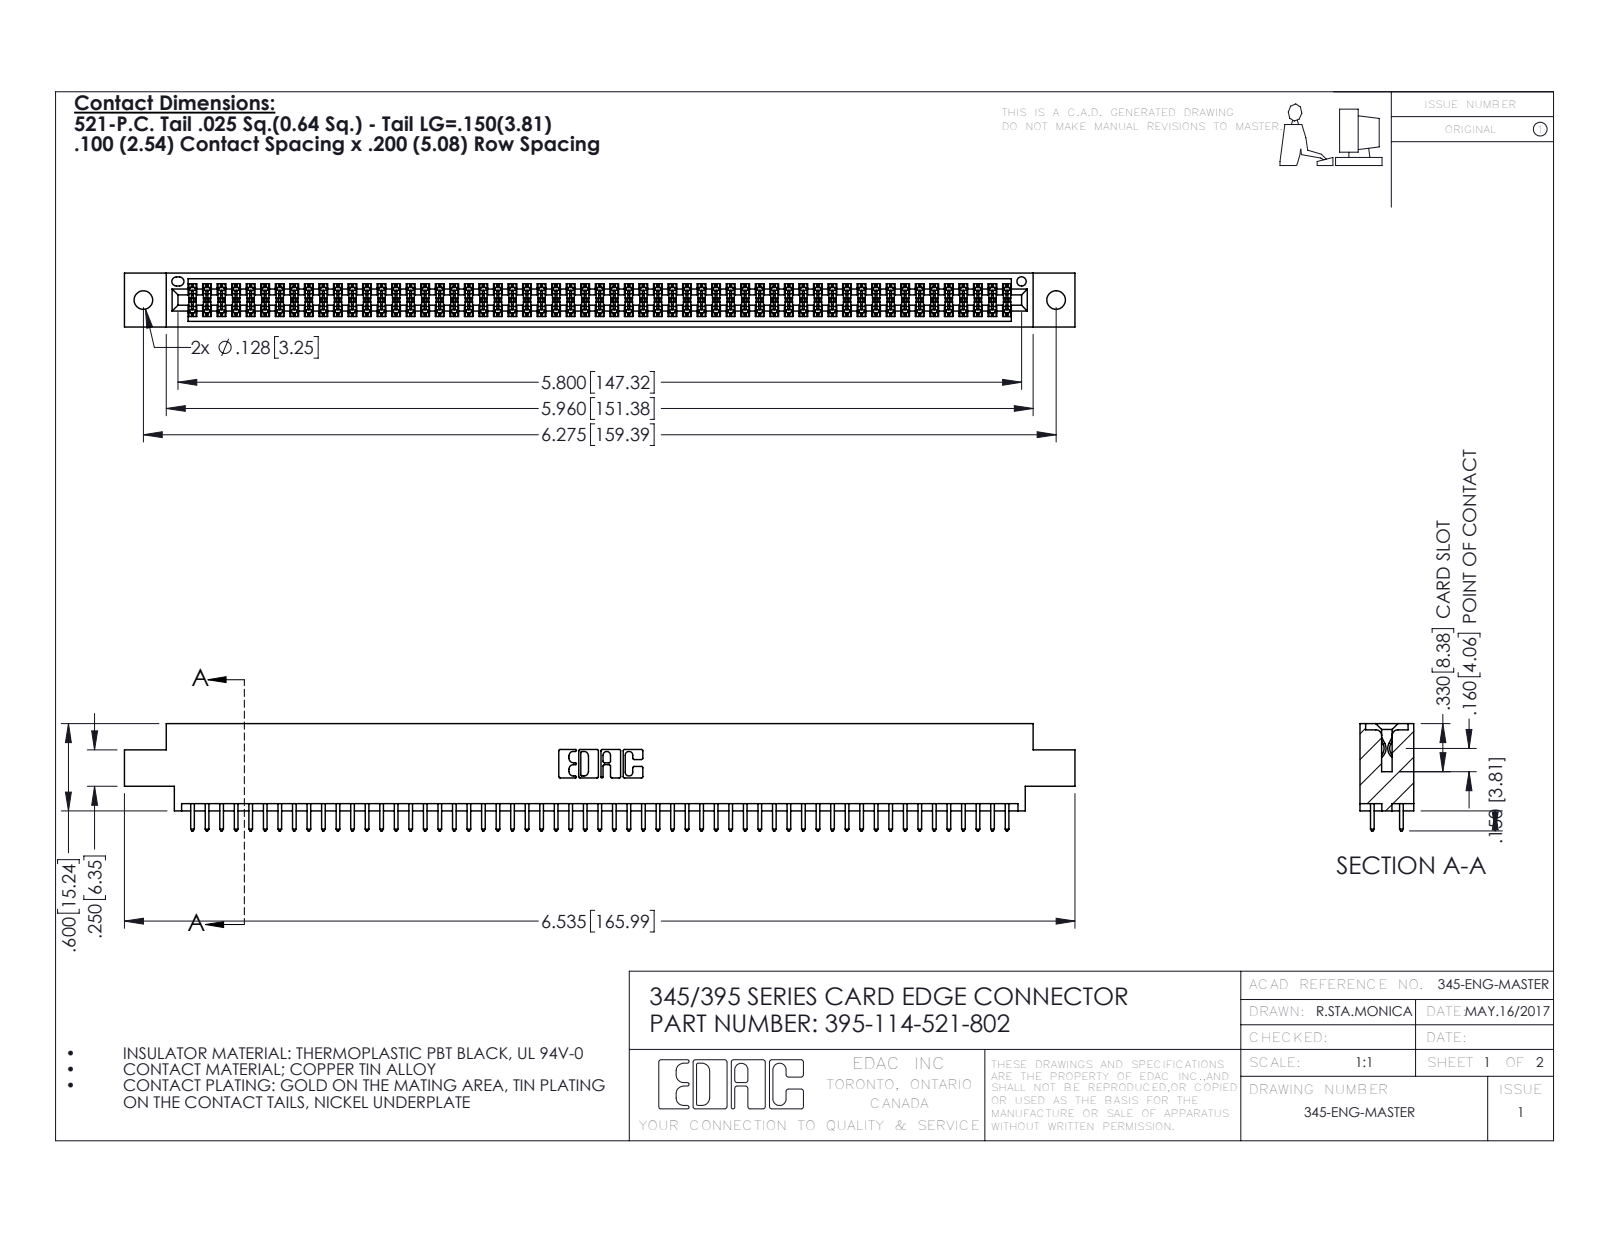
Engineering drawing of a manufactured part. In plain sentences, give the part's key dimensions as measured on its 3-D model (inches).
The part is named "345-292-001_345-293-121; 395-114-521-802; 345 Part_0.170 Offset - 0.128 Dia". Its 3-D file was written by "SolidWorks 2016 (CONFIG_CONTROL_DESIGN)". It is 115 solids with 5830 faces: 3846 planar, 1984 cylindrical and 0 other. Overall it measures 6.535 by 0.737 by 0.37 inches. Its volume is 0.98 cubic inches and its surface area 36.59 square inches. Round holes: 2 of diameter 0.128, 1 of diameter 0.064. Partial cylindrical surfaces (rounded edges, fillets, slot ends): 171 of radius 0.006, 114 of radius 0.01, 22 of radius 0.01, 6 of radius 0.007, 6 of radius 0.031, 3 of radius 0.026, 2 of radius 0.014, 2 of radius 0.019. The main face-to-face distances are 0.072, 0.298, 0.37, 0.2, 0.098, 0.272, 0.025, 0.225, 0.175, 0.149. The hole center spacings are 0.27, 6.039, 6.275.
